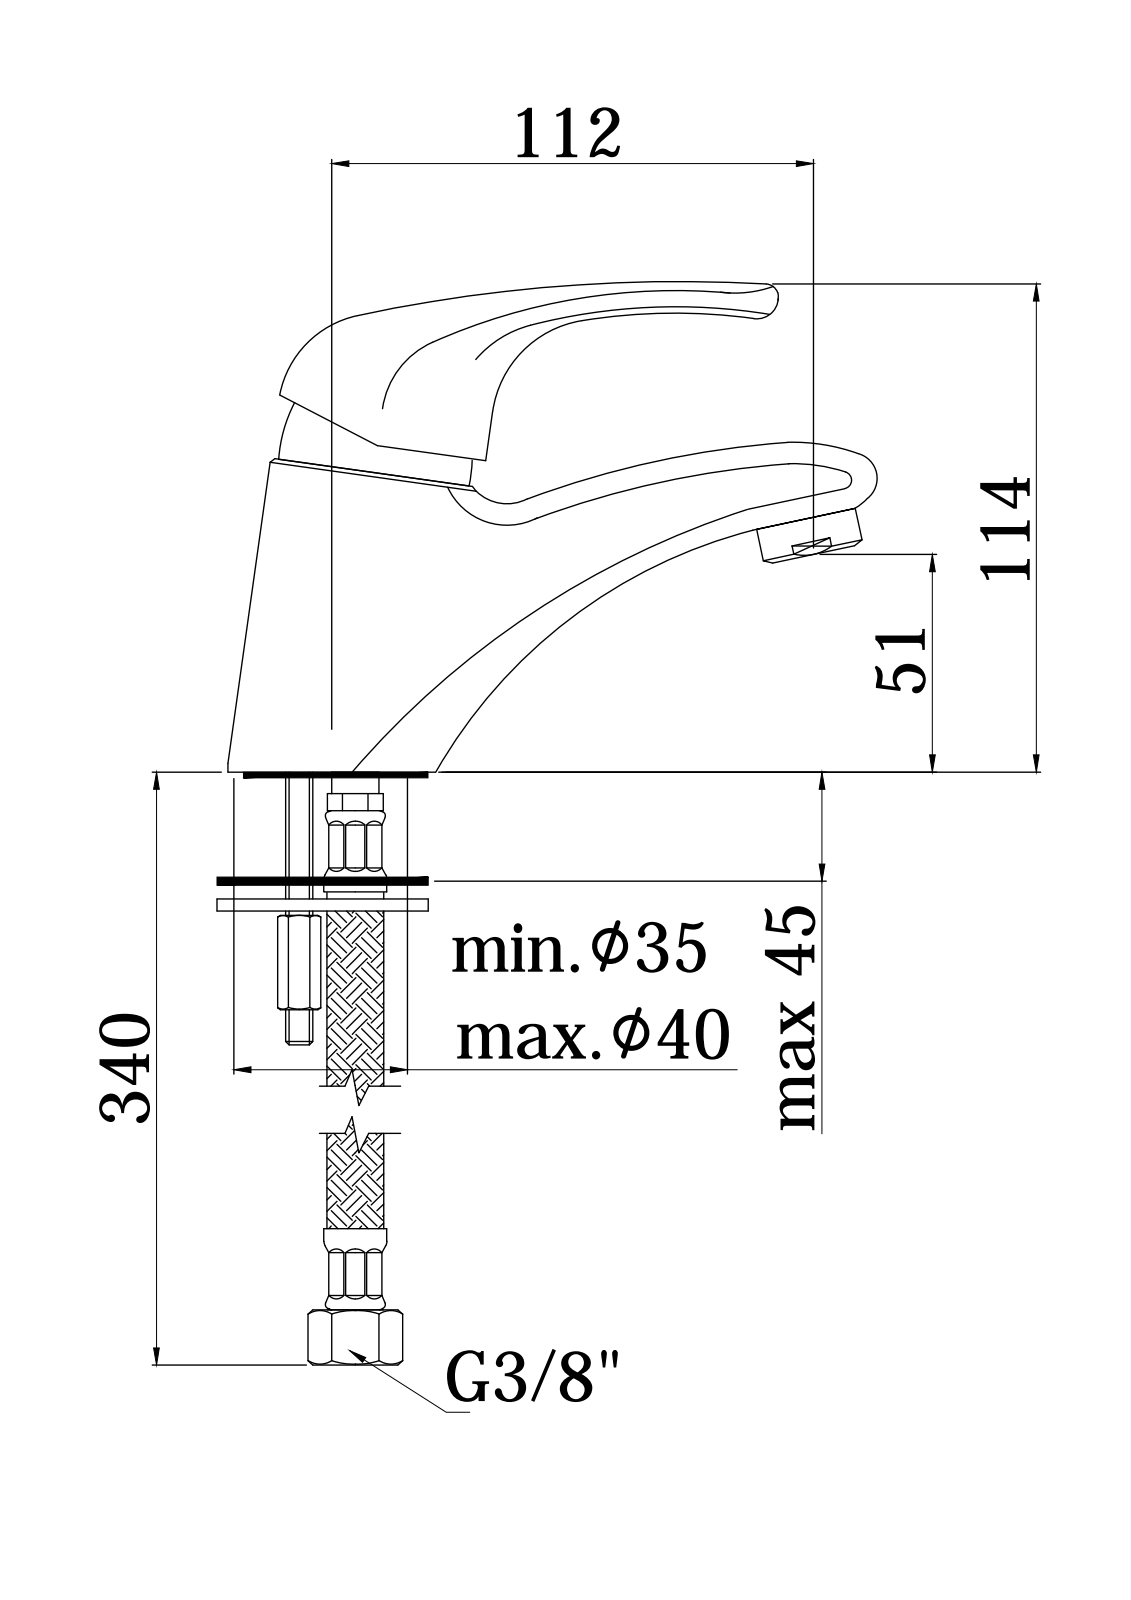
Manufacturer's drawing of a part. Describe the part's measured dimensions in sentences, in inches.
The part is named "ND071CR". Its 3-D file was written by "CREO PARAMETRIC BY PTC INC, 2020044 (CONFIG_CONTROL_DESIGN)". It is 1 solid with 179 faces: 58 planar, 46 cylindrical and 75 other. Overall it measures 6.019 by 4.629 by 2.008 inches. Its volume is 12.79 cubic inches and its surface area 82.26 square inches. Round holes: 2 of diameter 0.197, 2 of diameter 0.217, 2 of diameter 0.276, 2 of diameter 0.354, 2 of diameter 0.433, 2 of diameter 1.594, 1 of diameter 0.236, 1 of diameter 0.965, 1 of diameter 1.378, 1 of diameter 1.539, 1 of diameter 1.673. Round bosses or shafts: 1 of diameter 1.476, 1 of diameter 0.945, 1 of diameter 0.197. Partial cylindrical surfaces (rounded edges, fillets, slot ends): 1 of radius 0.154, 1 of radius 0.157. The main face-to-face distances are 2.399, 2.401, 0.059, 0.602, 3.001, 0.602, 0.6, 1.83, 0.569, 0.571. The hole center spacings are 0.339, 0.615, 0.338, 0.452, 0.465, 0.53, 0.615, 0.622.
